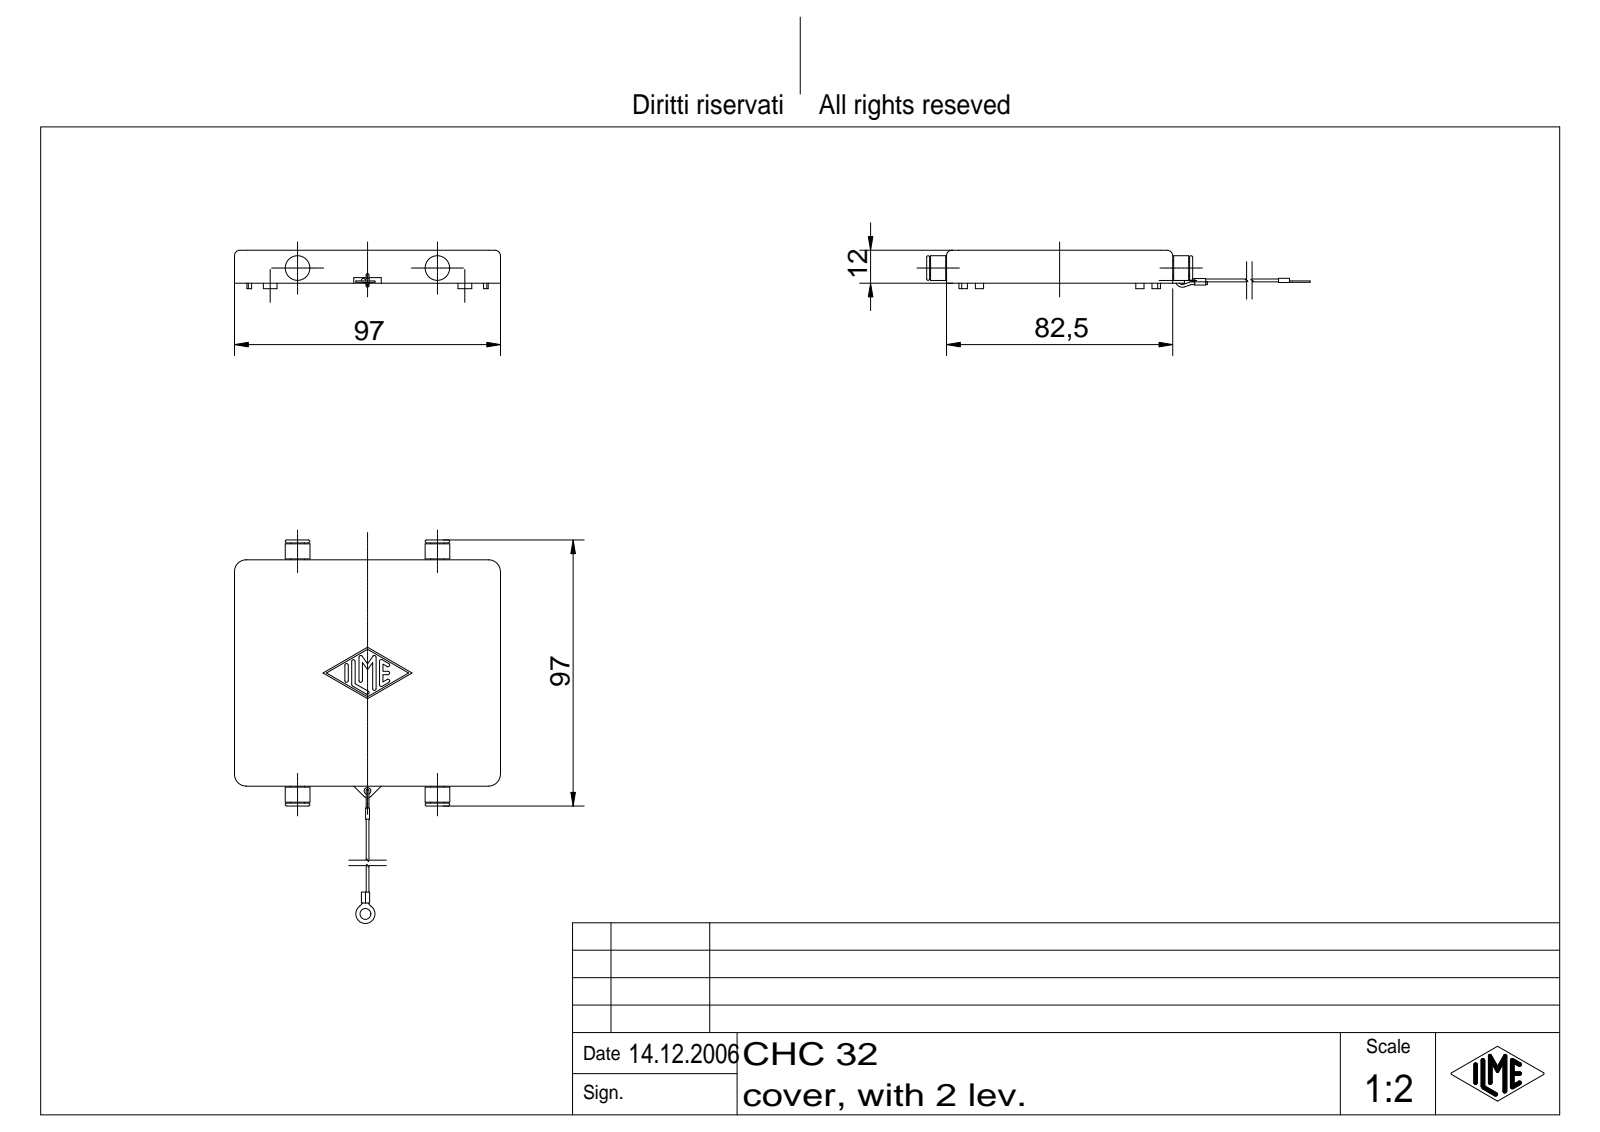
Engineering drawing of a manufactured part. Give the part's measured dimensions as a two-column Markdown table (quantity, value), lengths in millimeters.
| quantity | value |
| --- | --- |
| part name | CHC 32 |
| STEP written by | Autodesk Inventor 7 (AUTOMOTIVE_DESIGN) |
| units | millimeters |
| bodies | 2 solids, 258 faces (99 planar, 81 cylindrical, 78 other) |
| overall size | 214 × 97 × 14 |
| volume | 39 860 mm³ |
| surface area | 25 218 mm² |
| round holes (diameter × count) | 2.5 × 1, 4 × 1 |
| round bosses / shafts (diameter × count) | 1 × 4, 9 × 2, 5 × 2, 7 × 1 |
| partial cylindrical surfaces (radius × count) | 0.62 × 14, 2 × 8, 0.7 × 4, 4.3 × 4, 0.75 × 2, 1 × 2, 3 × 2, 1.75 × 1 |
| main face-to-face distances | 3, 4.5, 9, 12, 78, 92.5, 82.5, 97, 73.5, 88 |
| hole center spacings | 119 |
